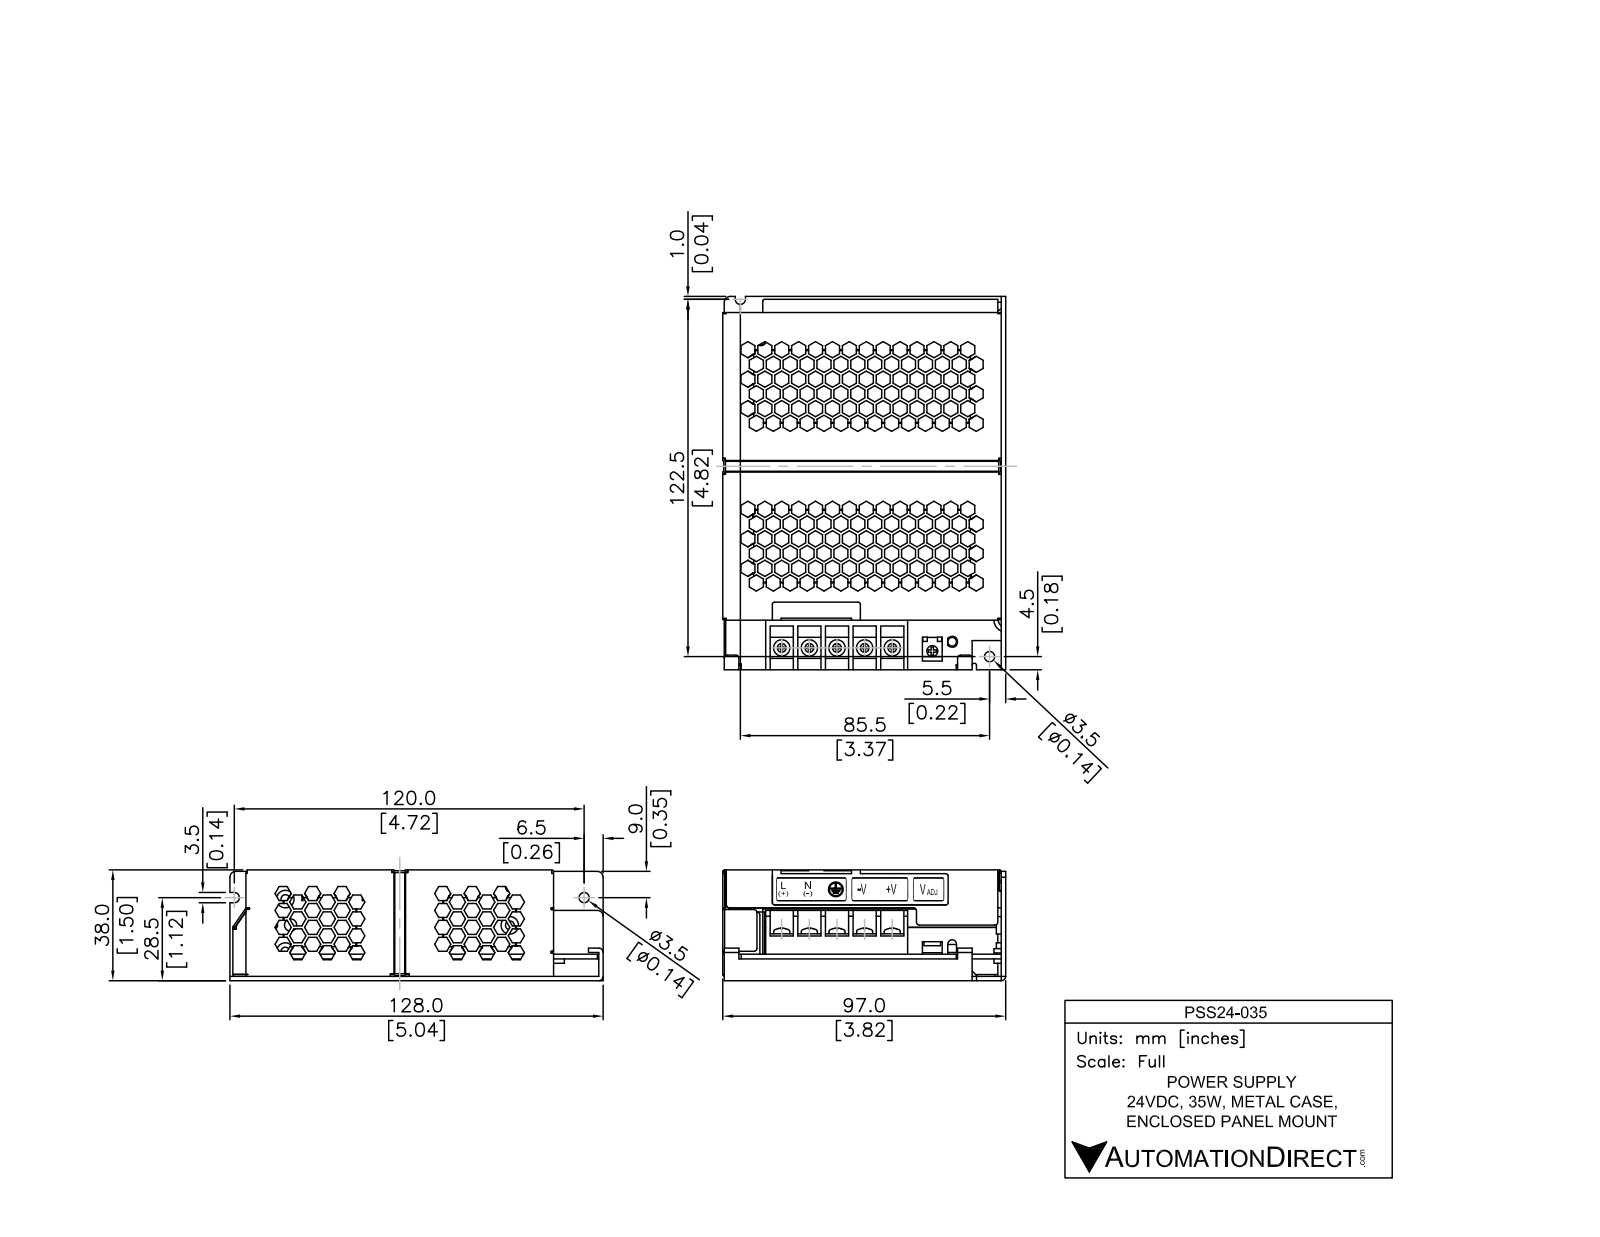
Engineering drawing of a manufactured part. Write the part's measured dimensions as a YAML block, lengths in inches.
part_name: "PSS 24-035"
step_written_by: "SolidWorks 2011 (CONFIG_CONTROL_DESIGN)"
units: inches
bodies: {solids: 3, faces: 1670, planar: 1540, cylindrical: 68, other: 62}
overall_size: [5.04, 3.82, 1.501]
volume: 10.02
surface_area: 156.3
round_holes:
  - {diameter: 0.13, count: 2}
round_bosses_or_shafts:
  - {diameter: 0.22, count: 5}
  - {diameter: 0.028, count: 2}
  - {diameter: 0.274, count: 1}
  - {diameter: 0.124, count: 1}
  - {diameter: 0.07, count: 1}
  - {diameter: 0.068, count: 1}
partial_cylinders:
  - {radius: 0.03, count: 7}
  - {radius: 0.04, count: 5}
  - {radius: 0.05, count: 5}
  - {radius: 0.06, count: 4}
  - {radius: 0.015, count: 2}
  - {radius: 0.07, count: 2}
  - {radius: 0.175, count: 2}
  - {radius: 0.1, count: 1}
face_to_face_distances: [0.03, 1.47, 0.385, 1.085, 0.327, 1.44, 0.297, 0.058, 0.355, 1.115]
